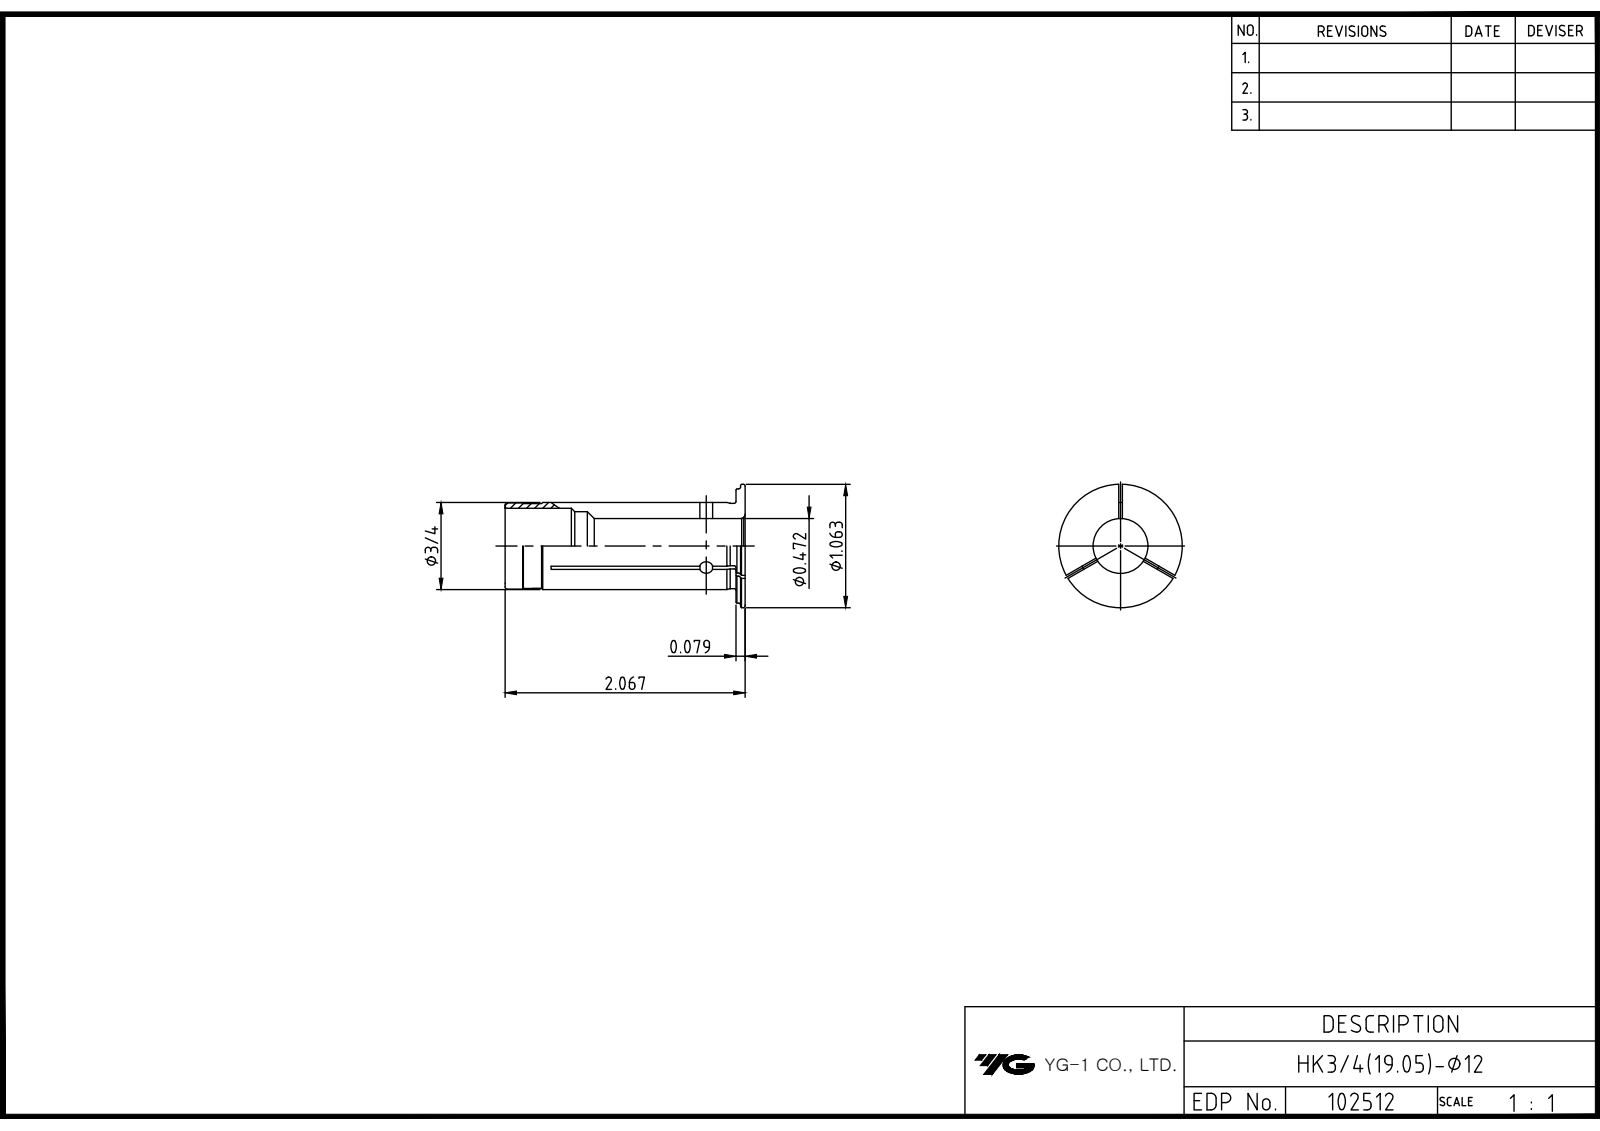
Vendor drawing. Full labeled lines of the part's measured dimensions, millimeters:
Part name (STEP PRODUCT): LO-HK19.05-12
STEP written by: Autodesk Inventor 2022 (AUTOMOTIVE_DESIGN)
Units: millimetres
Bodies: 1 solid, 29 faces (4 planar, 9 cylindrical, 16 other)
Overall size (bounding box): 52.5 × 27 × 27
Volume: 7 656 mm³ · Surface area: 6 181 mm²
Round holes (diameter × count): ⌀12 ×1, ⌀15 ×1, ⌀16.5 ×1
Round bosses / shafts (diameter × count): ⌀27 ×1, ⌀25 ×1, ⌀19.05 ×1, ⌀18.85 ×1, ⌀18.65 ×1, ⌀18.55 ×1
Main face-to-face distances: 2, 1, 50.5, 51.5, 52.5
